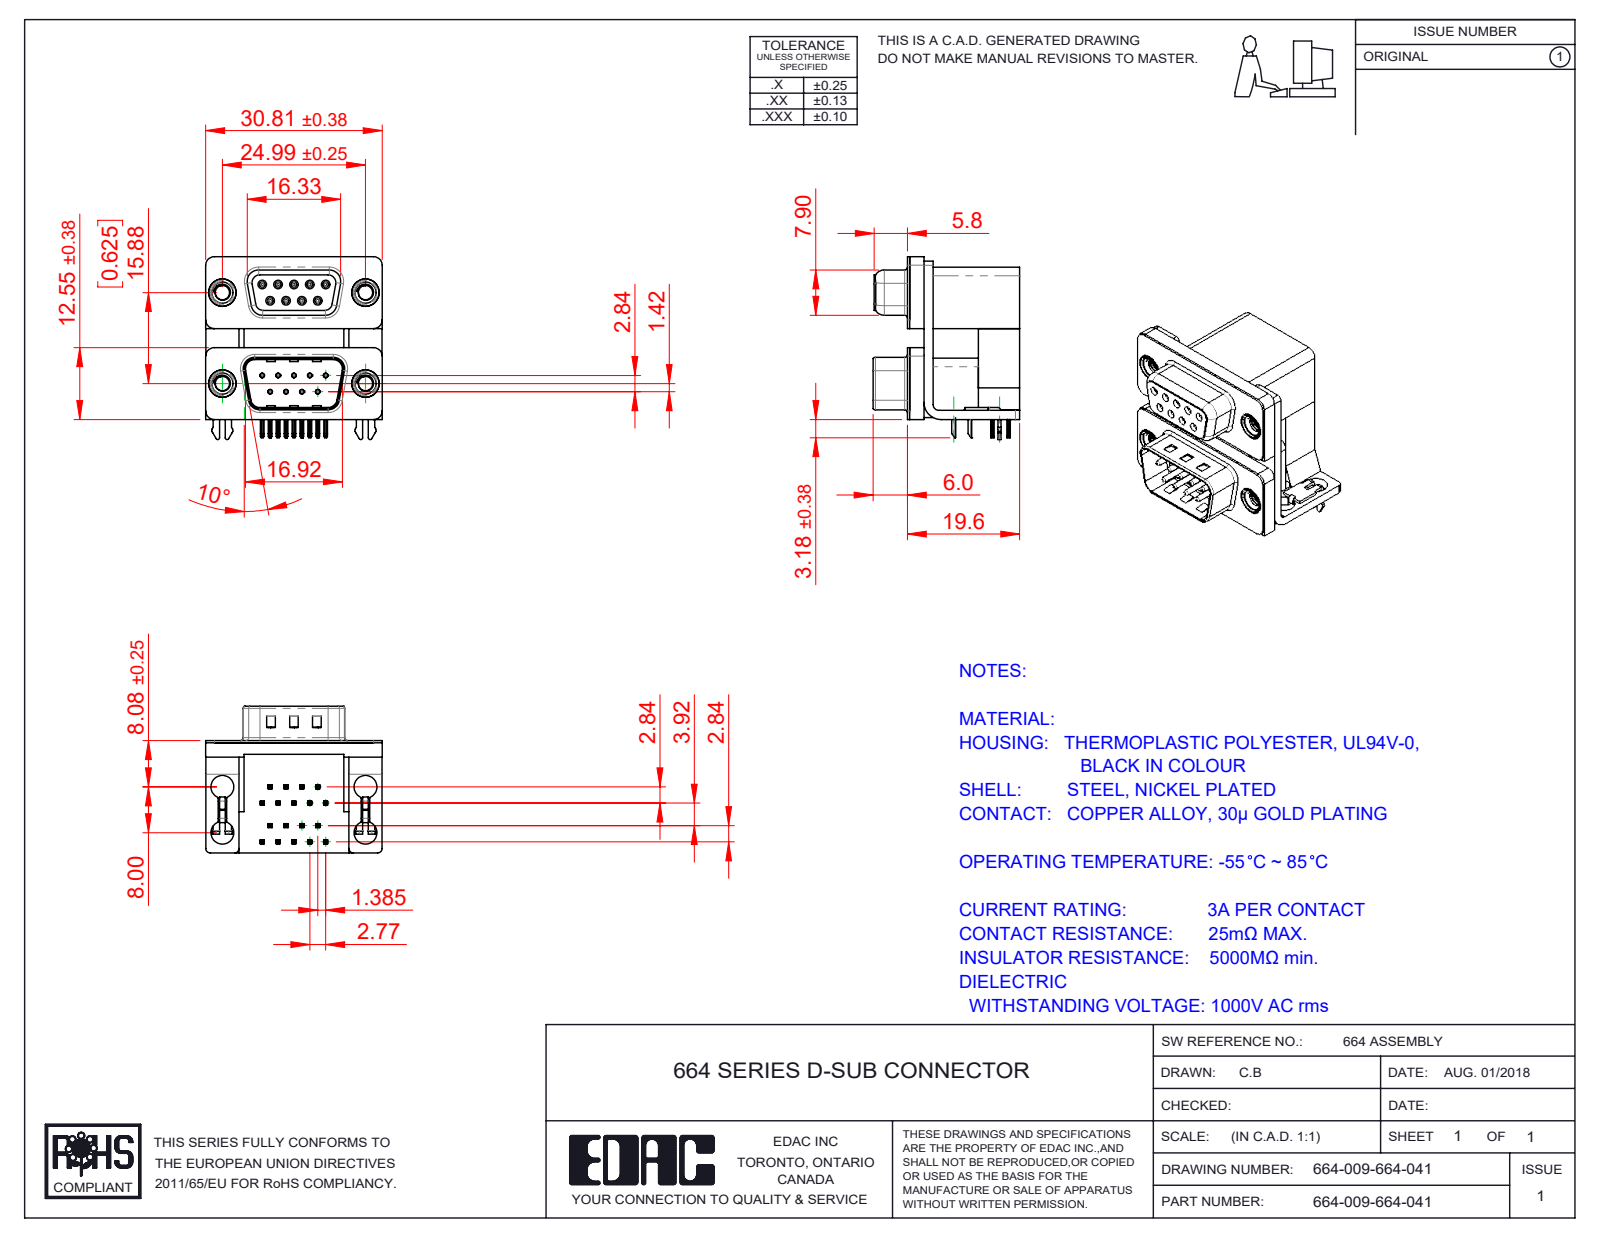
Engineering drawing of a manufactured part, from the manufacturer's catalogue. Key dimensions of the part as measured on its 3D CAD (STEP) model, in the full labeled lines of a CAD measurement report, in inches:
Part name (STEP PRODUCT): 664 Housing Lower_09 Contacts; 664 Mounting Bracket_2ProngL; 664-009-664-041; 664 Threaded Rivet_M3 (+8 more)
STEP written by: SolidWorks 2020 (CONFIG_CONTROL_DESIGN)
Units: inches
Bodies: 31 solids, 2641 faces (1341 planar, 733 cylindrical, 567 other)
Overall size (bounding box): 1.257 × 1.213 × 1.008
Volume: 0.629 in³ · Surface area: 19.05 in²
Round holes (diameter × count): ⌀0.031 ×18, ⌀0.014 ×9, ⌀0.035 ×9, ⌀0.157 ×8, ⌀0.098 ×4, ⌀0.138 ×4, ⌀0.189 ×4, ⌀0.197 ×4
Round bosses / shafts (diameter × count): ⌀0.047 ×9, ⌀0.03 ×9, ⌀0.193 ×4, ⌀0.187 ×4, ⌀0.154 ×4
Partial cylindrical surfaces — rounded edges, fillets, slot ends (radius × count): R0.004 ×73, R0.01 ×42, R0.006 ×36, R0.005 ×18, R0.014 ×18, R0.02 ×16, R0.059 ×13, R0.03 ×10
Main face-to-face distances: 0.016, 0.098, 0.657, 0.756, 0.772, 0.114, 0.283, 0.374, 0.472, 0.488
Hole centre spacings: 0.124, 0.109, 0.635, 0.625, 0.218, 0.662, 0.516, 0.739
